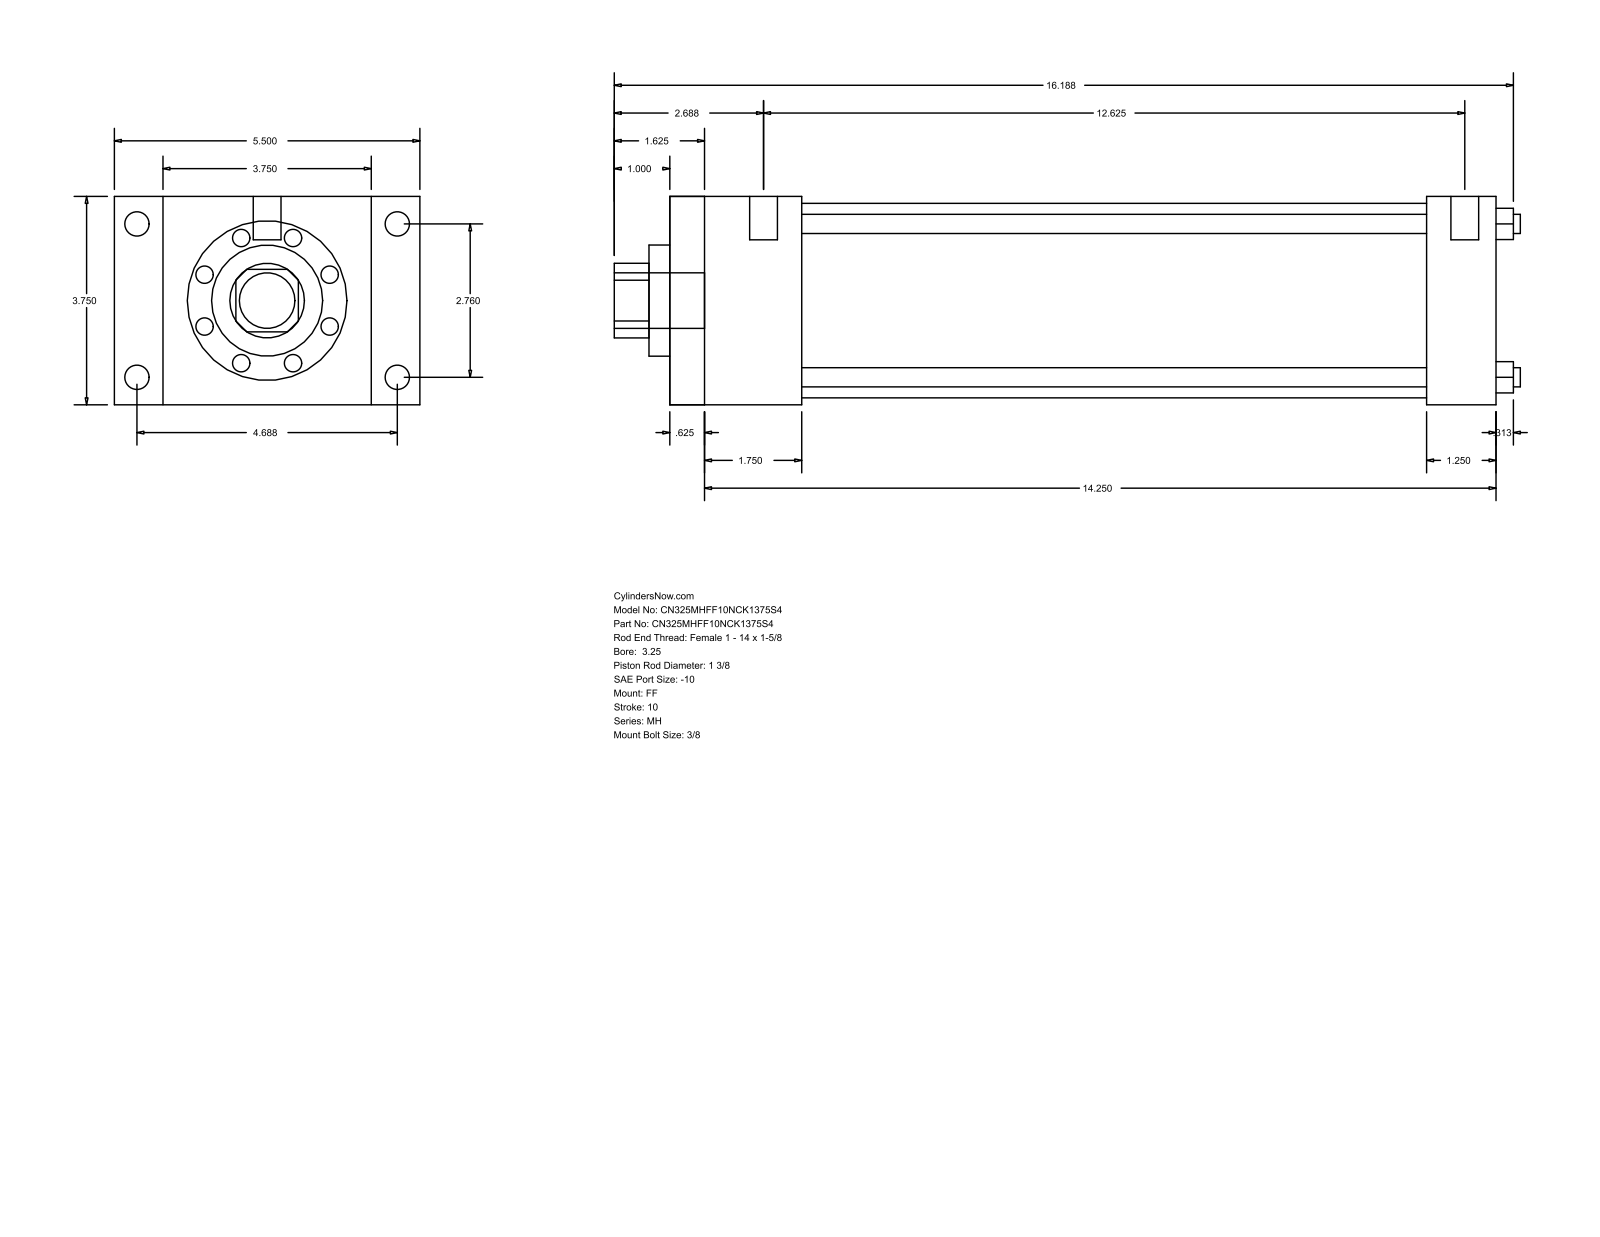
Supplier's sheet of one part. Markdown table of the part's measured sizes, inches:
| quantity | value |
| --- | --- |
| part name | MH_FF__0325_1.375 |
| STEP written by | GSSL Pune (CONFIG_CONTROL_DESIGN) |
| units | inches |
| bodies | 0 solids, 92 faces (64 planar, 28 cylindrical, 0 other) |
| overall size | 16.313 × 5.5 × 3.75 |
| round holes (diameter × count) | 0.345 × 4, 1.375 × 1, 2 × 1, 3.5 × 1 |
| round bosses / shafts (diameter × count) | 0.438 × 4, 0.219 × 4, 0.5 × 2, 1 × 1 |
| partial cylindrical surfaces (radius × count) | 0.672 × 1 |
| main face-to-face distances | 3.75, 14.875, 0.625, 14.25, 0.875, 4.625, 13.625, 13, 1.25, 2.375 |
| hole center spacings | 1.952, 2.76, 3.903 |
